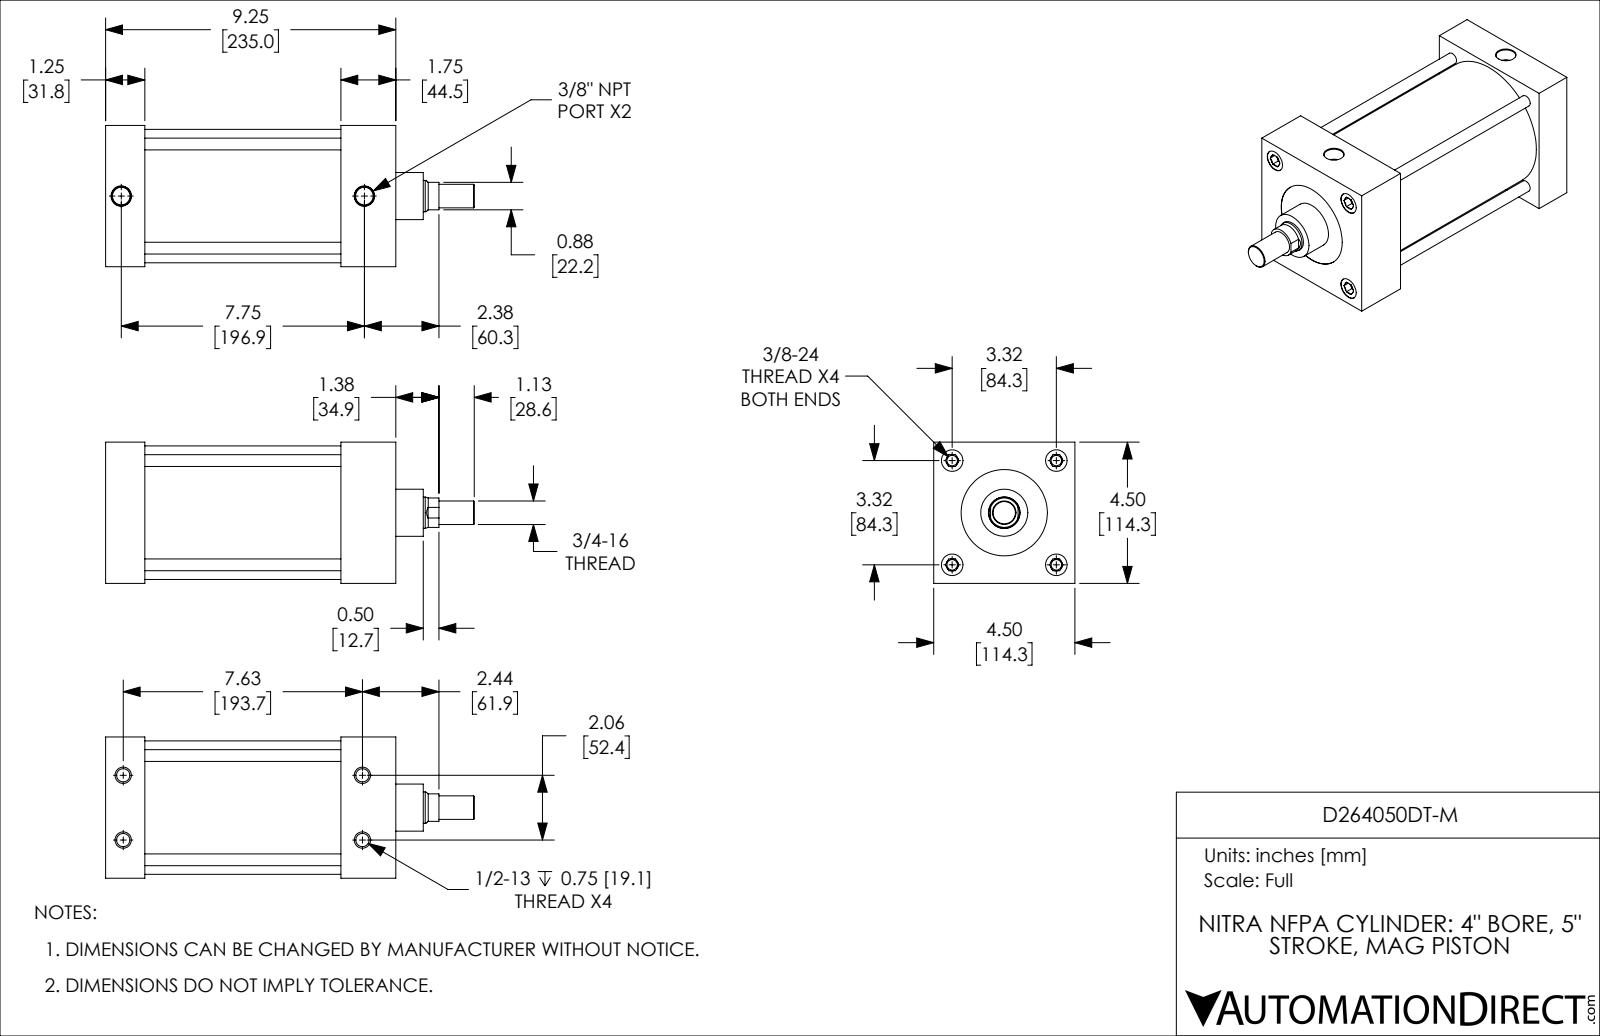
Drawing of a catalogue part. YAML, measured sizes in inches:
part_name: "D264050DT-M; D264050DT-M_BODY; D264050DT-M_PISTON_KK1"
step_written_by: "SolidWorks 2019 (CONFIG_CONTROL_DESIGN)"
units: inches
bodies: {solids: 2, faces: 198, planar: 58, cylindrical: 62, other: 78}
overall_size: [11.75, 4.5, 4.5]
volume: 93.27
surface_area: 421.9
round_holes:
  - {diameter: 0.332, count: 4}
  - {diameter: 0.422, count: 4}
  - {diameter: 0.687, count: 4}
  - {diameter: 0.562, count: 2}
  - {diameter: 1.001, count: 1}
  - {diameter: 2.75, count: 1}
  - {diameter: 4.001, count: 1}
round_bosses_or_shafts:
  - {diameter: 0.375, count: 4}
  - {diameter: 4.251, count: 1}
  - {diameter: 3.999, count: 1}
  - {diameter: 1.5, count: 1}
  - {diameter: 0.999, count: 1}
  - {diameter: 0.75, count: 1}
partial_cylinders:
  - {radius: 0.469, count: 1}
face_to_face_distances: [1.25, 4.5, 7.5, 6.25, 9.25, 8, 1.75, 2.5, 5, 6.75]
hole_center_spacings: [2.347, 3.32, 7.756, 1.033, 4.695, 7.625, 7.899, 1.034]
